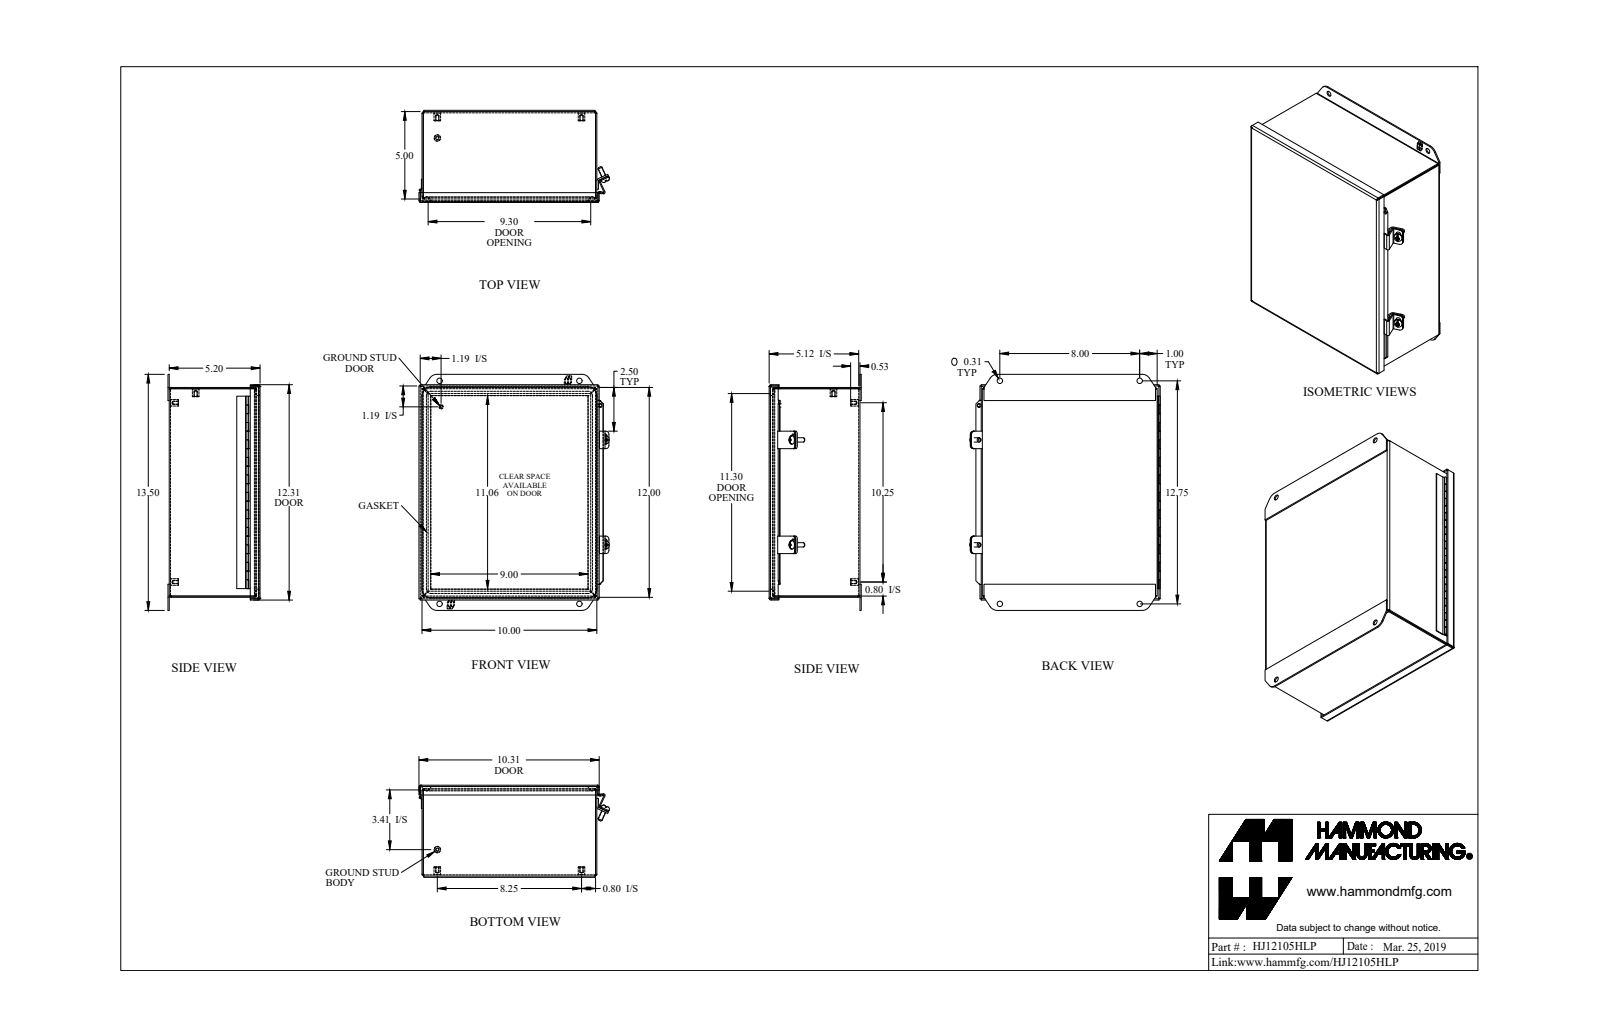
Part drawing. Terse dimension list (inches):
name: HJ12105HLP
written by: SolidWorks 2018 (AUTOMOTIVE_DESIGN)
unit: in
bodies: 20 solids, 773 faces (414 planar, 232 cylindrical, 127 other)
size: 13.5 × 10.896 × 5.269
volume: 42.88 in³; area: 1 205 in²
holes: 5× ⌀0.156, 4× ⌀0.313, 2× ⌀0.213, 1× ⌀0.05
bosses: 5× ⌀0.375, 3× ⌀0.25, 2× ⌀0.48, 1× ⌀0.188, 1× ⌀0.1, 1× ⌀0.045
rounds: 16× R0.25, 13× R0.036, 13× R0.108, 8× R0.188, 4× R0.01, 4× R0.141, 4× R0.499, 4× R0.5
face distances: 0.072, 5.125, 5.197, 5.053, 9.928, 11.928, 10, 9.856, 12, 11.856
hole spacings: 1.256, 8.22, 11.501, 14.081, 8, 8.25, 10.25, 12.75
